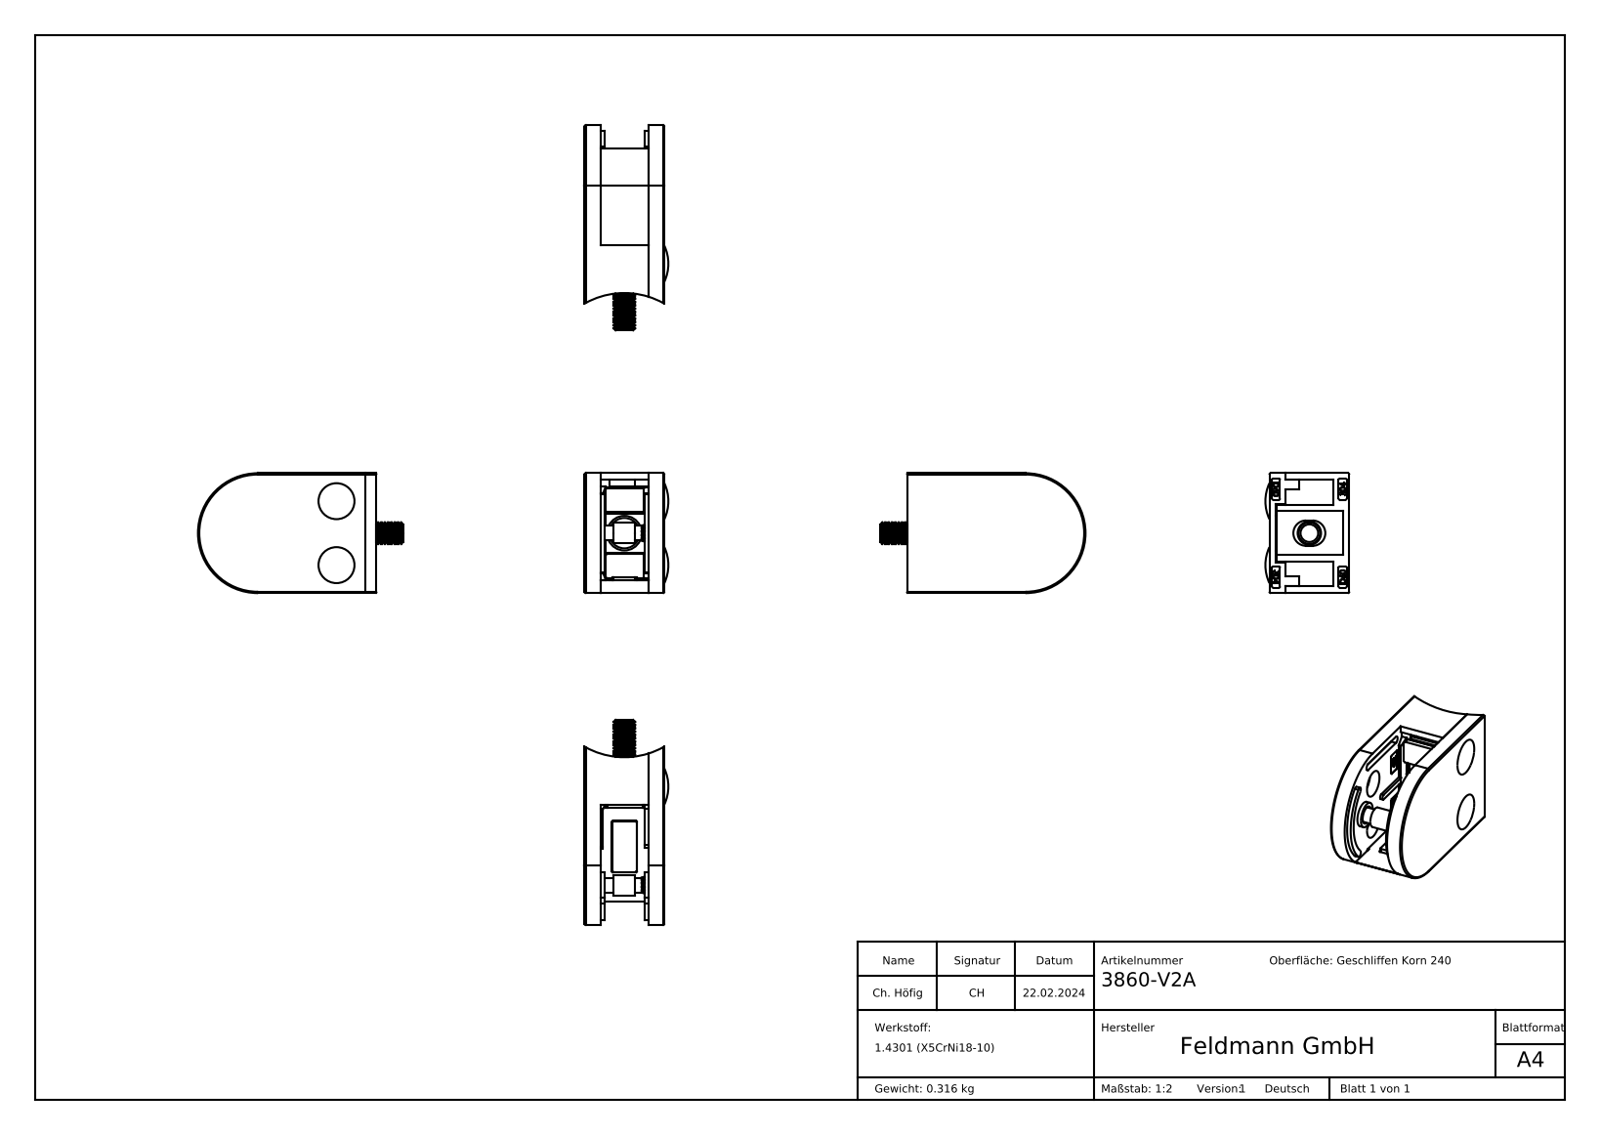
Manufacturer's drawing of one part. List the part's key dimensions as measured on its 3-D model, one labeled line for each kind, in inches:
Part name (STEP PRODUCT): 38-Kappe_GK-P-G; socket countersunk head screw_din_DIN 7991 - M6 x 16 --- 16S; 38xx-XXX Teil2_3860-V2A; 38-STIFT_38-STIFT (+8 more)
STEP written by: SolidWorks 2018 (CONFIG_CONTROL_DESIGN)
Units: inches
Bodies: 13 solids, 1825 faces (950 planar, 197 cylindrical, 678 other)
Overall size (bounding box): 3.031 × 1.772 × 1.24
Volume: 2.661 in³ · Surface area: 43.31 in²
Round holes (diameter × count): ⌀0.079 ×2, ⌀0.197 ×2, ⌀0.252 ×2, ⌀0.394 ×2, ⌀0.48 ×2, ⌀0.22 ×1, ⌀0.264 ×1
Round bosses / shafts (diameter × count): ⌀0.456 ×2, ⌀0.236 ×2, ⌀0.512 ×1, ⌀0.374 ×1, ⌀0.315 ×1, ⌀0.299 ×1
Partial cylindrical surfaces — rounded edges, fillets, slot ends (radius × count): R0.02 ×56, R0.039 ×4, R0.053 ×4, R0.047 ×2, R0.187 ×2, R0.118 ×1, R0.713 ×1, R0.807 ×1
Main face-to-face distances: 0.945, 0.236, 1.181, 0.709, 0.079, 0.098, 0.138, 1.772, 0.02, 0.157
Hole centre spacings: 0.474, 1.148, 1.41, 1.531, 0.709, 0.945
